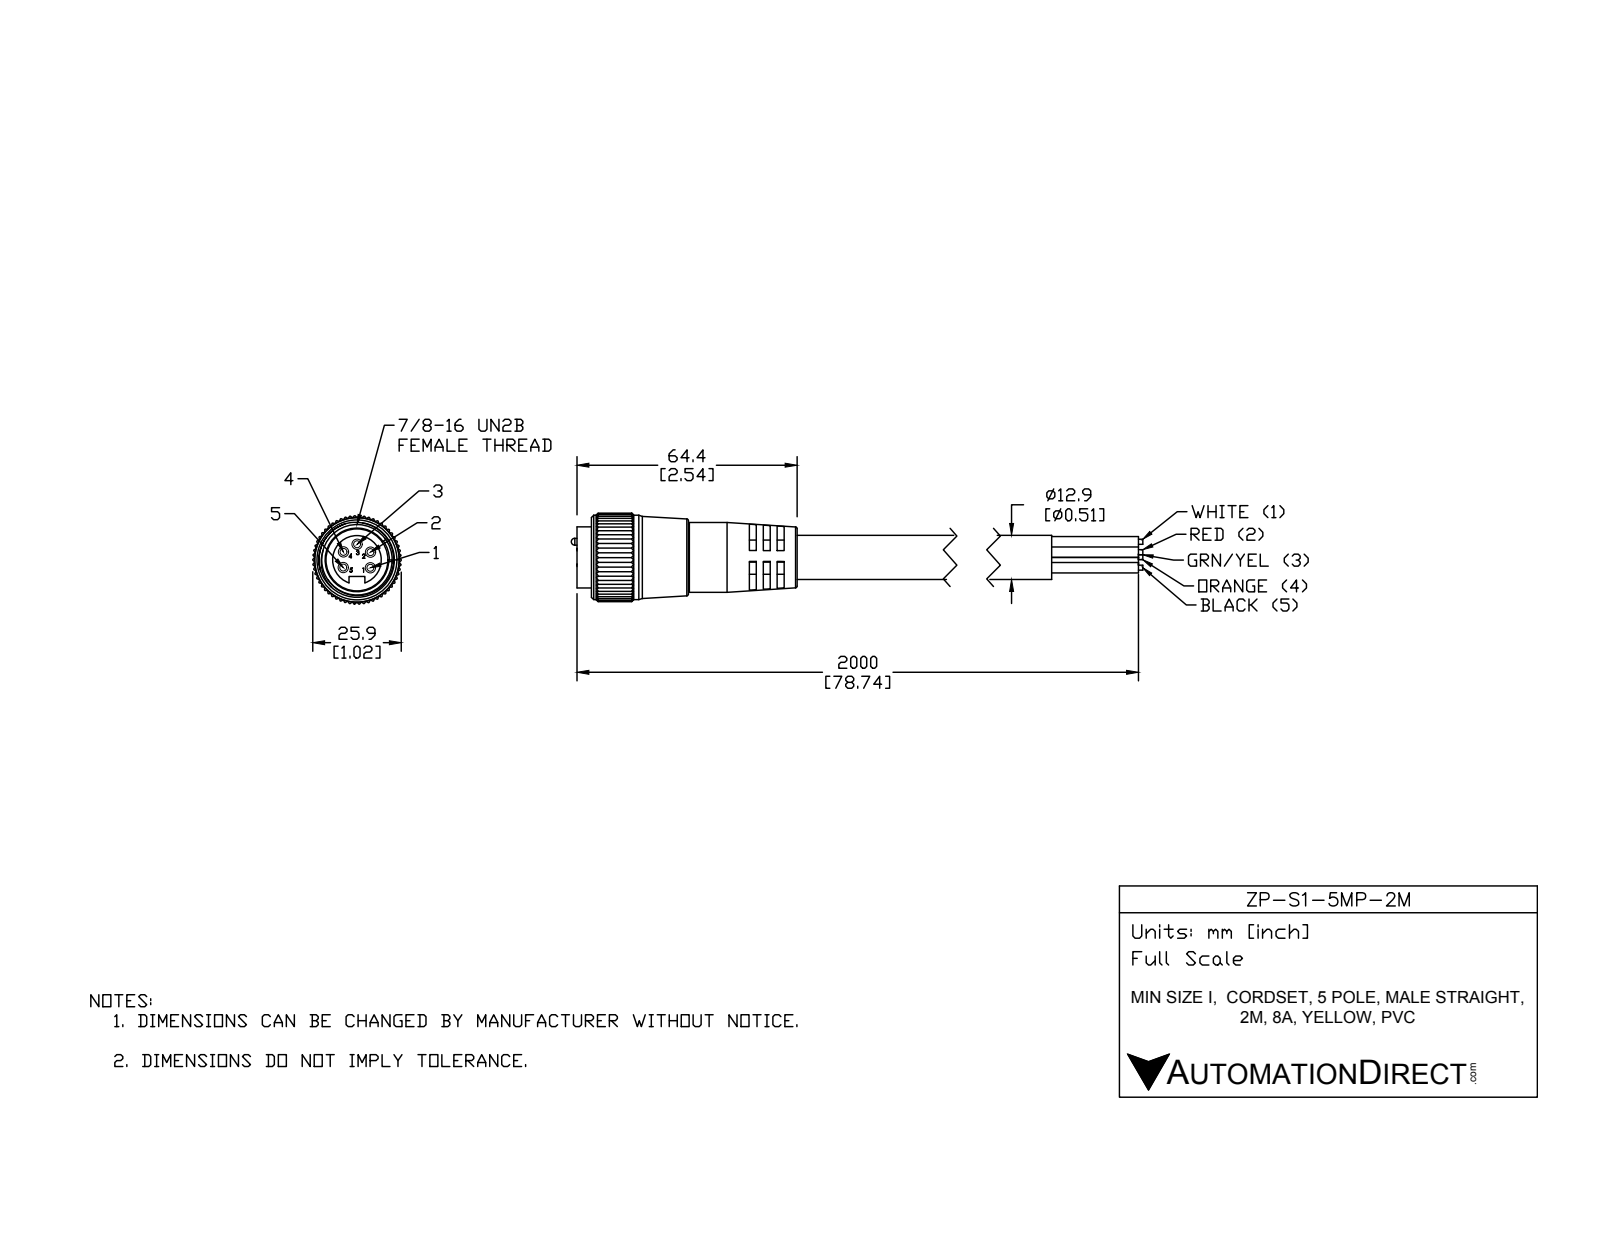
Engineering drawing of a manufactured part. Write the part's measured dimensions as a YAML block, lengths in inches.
part_name: "ZP-S1-5MP-2M"
step_written_by: "SolidWorks 2015 (AUTOMOTIVE_DESIGN)"
units: inches
bodies: {solids: 7, faces: 614, planar: 222, cylindrical: 322, other: 70}
overall_size: [4.376, 2.083, 1.017]
volume: 1.888
surface_area: 20.76
round_holes:
  - {diameter: 0.56, count: 1}
  - {diameter: 0.786, count: 1}
  - {diameter: 0.805, count: 1}
  - {diameter: 0.827, count: 1}
round_bosses_or_shafts:
  - {diameter: 0.12, count: 5}
  - {diameter: 0.079, count: 5}
  - {diameter: 0.509, count: 2}
  - {diameter: 0.972, count: 1}
  - {diameter: 0.803, count: 1}
  - {diameter: 0.768, count: 1}
  - {diameter: 0.704, count: 1}
partial_cylinders:
  - {radius: 0.01, count: 165}
  - {radius: 0.09, count: 1}
  - {radius: 0.207, count: 1}
  - {radius: 0.509, count: 1}
face_to_face_distances: [0.079, 0.159, 0.08, 0.238, 0.158, 0.239, 0.317, 0.08, 0.396, 0.318]
